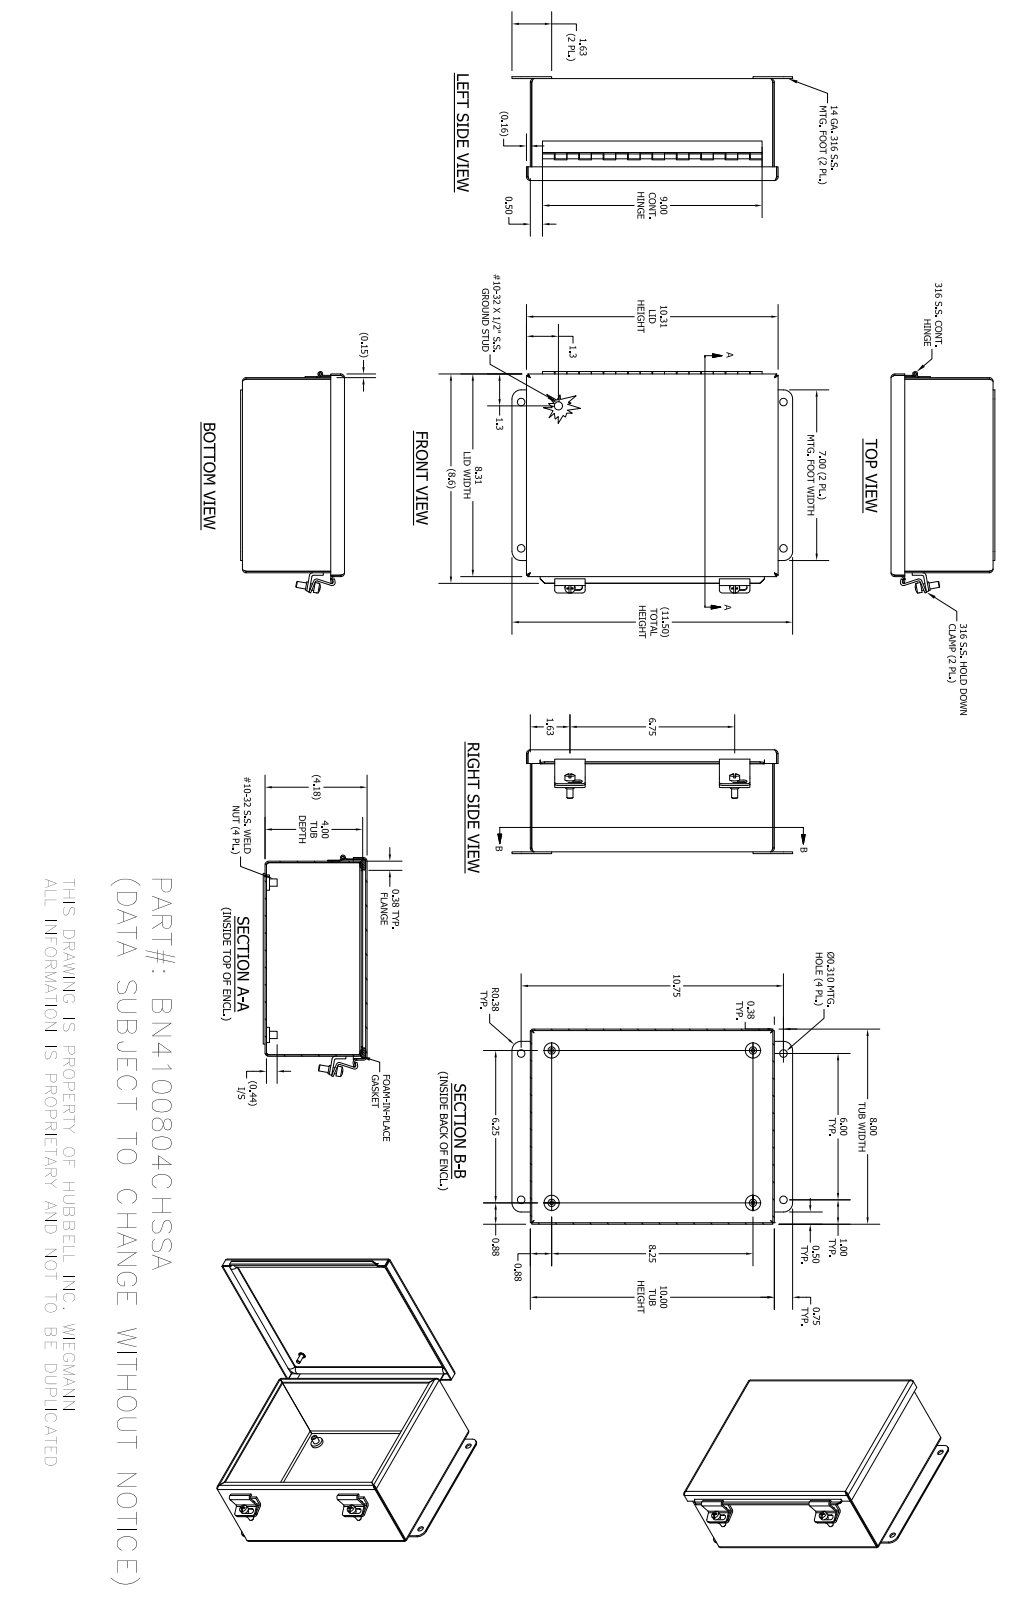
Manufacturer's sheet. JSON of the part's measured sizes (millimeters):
{"part_name": "B_100804_SSABKP; 32883LH; 32883P; 32883TH (+8 more)", "step_written_by": "Autodesk Inventor 2016 (AUTOMOTIVE_DESIGN)", "units": "millimeters", "bodies": {"solids": 19, "faces": 448, "planar": 244, "cylindrical": 137, "other": 67}, "overall_size": [292.1, 230.78, 108.11], "volume_mm3": 423140, "surface_area_mm2": 526382, "round_holes": [[2.79, 4], [3.96, 4], [7.87, 4], [4.98, 2], [2.96, 1]], "round_bosses_or_shafts": [[15.88, 4], [7.62, 4], [10.4, 2], [8.74, 2], [6.35, 2], [8.56, 1], [5.08, 1], [4.83, 1]], "partial_cylinders_radius": [[2.38, 13], [3.88, 13], [1.68, 8], [3.17, 8], [3.38, 4], [5.78, 4], [9.53, 4], [1.6, 3]], "face_to_face_distances": [1.5, 104.71, 106.21, 103.21, 201.7, 252.5, 203.2, 200.2, 254, 251], "hole_center_spacings": [31.91, 152.4, 171.45, 241.32, 19.05, 158.75, 158.79, 209.55]}
